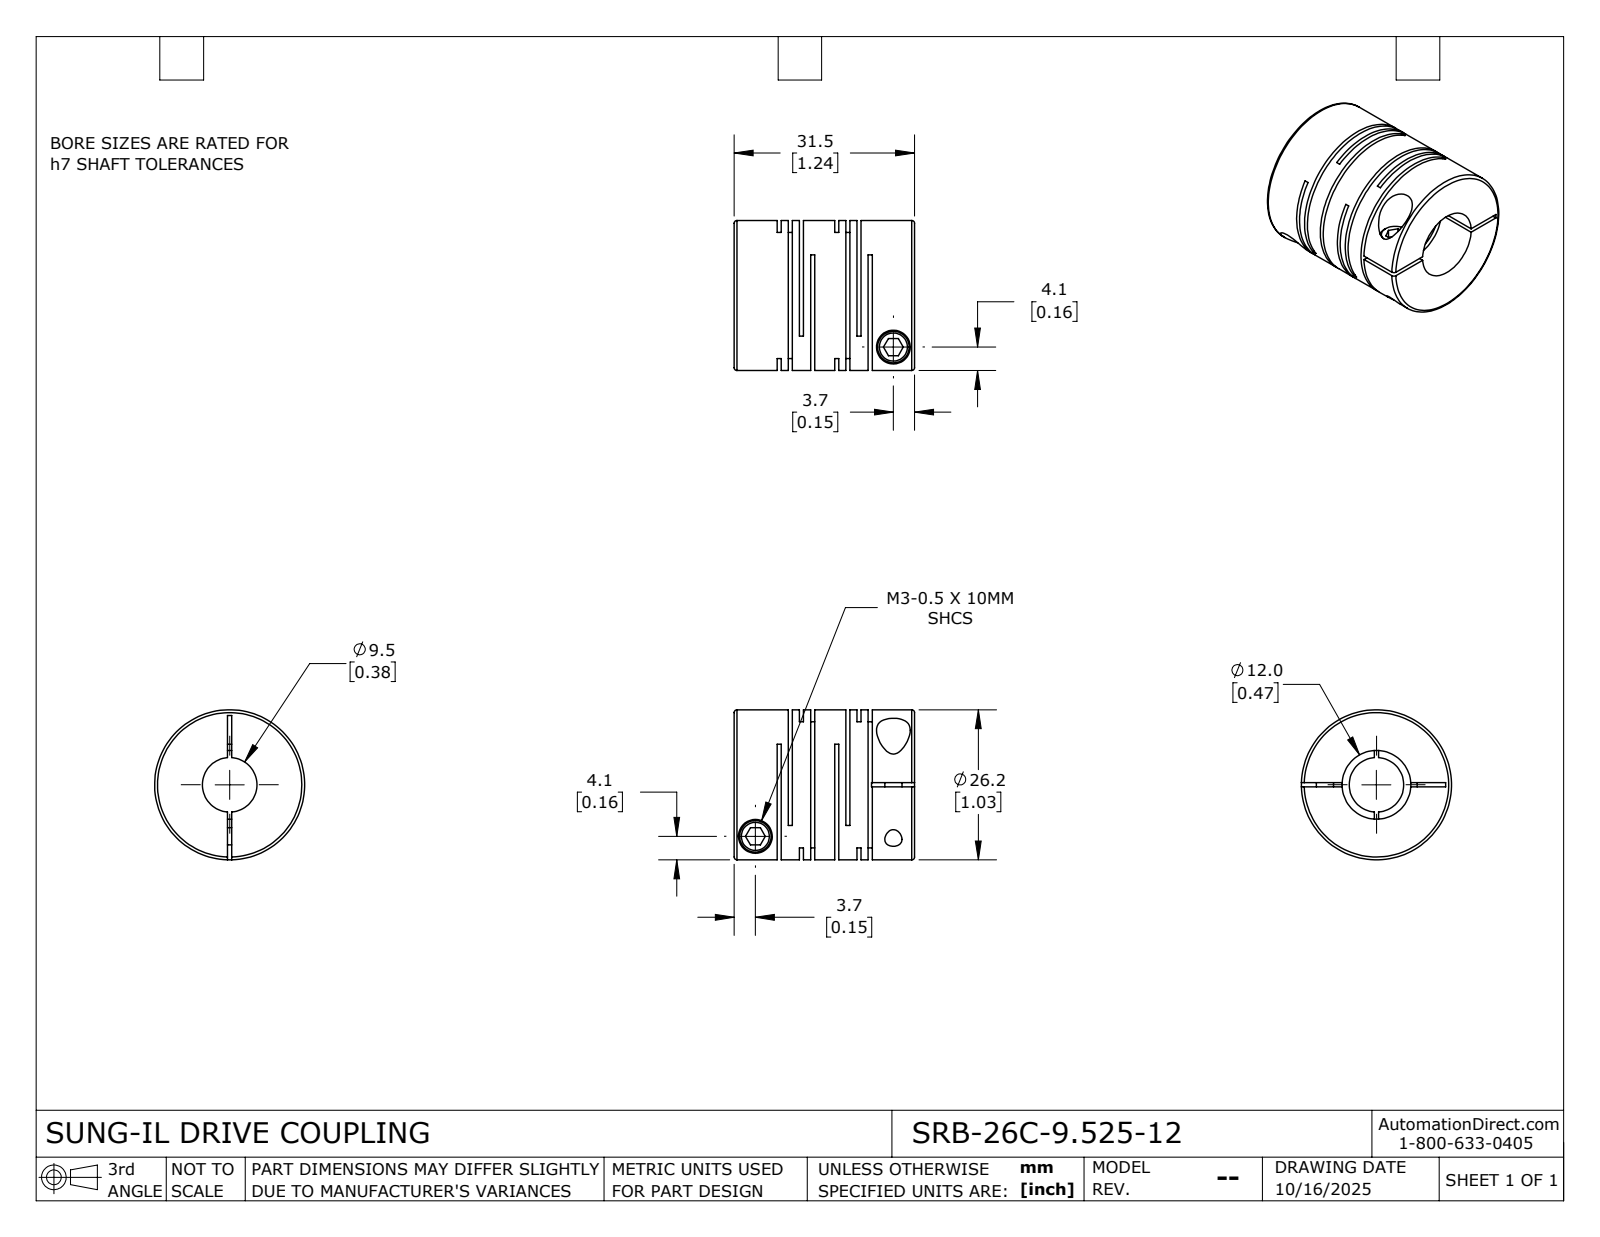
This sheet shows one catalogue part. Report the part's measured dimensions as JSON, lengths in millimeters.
{"part_name": "SRB-26C-9.525-12", "step_written_by": "SolidWorks 2024 (CONFIG_CONTROL_DESIGN)", "units": "millimeters", "bodies": {"solids": 1, "faces": 115, "planar": 60, "cylindrical": 42, "other": 13}, "overall_size": [31.5, 26.2, 26.2], "volume_mm3": 11372, "surface_area_mm2": 10269, "round_holes": [[3, 2], [5.9, 2], [9.53, 1], [12, 1]], "round_bosses_or_shafts": [[5.5, 2], [26.2, 1]], "face_to_face_distances": [1.95, 10.05, 0.71, 3.9, 8.1, 12, 1.24, 2.66, 9.34, 13.95]}
